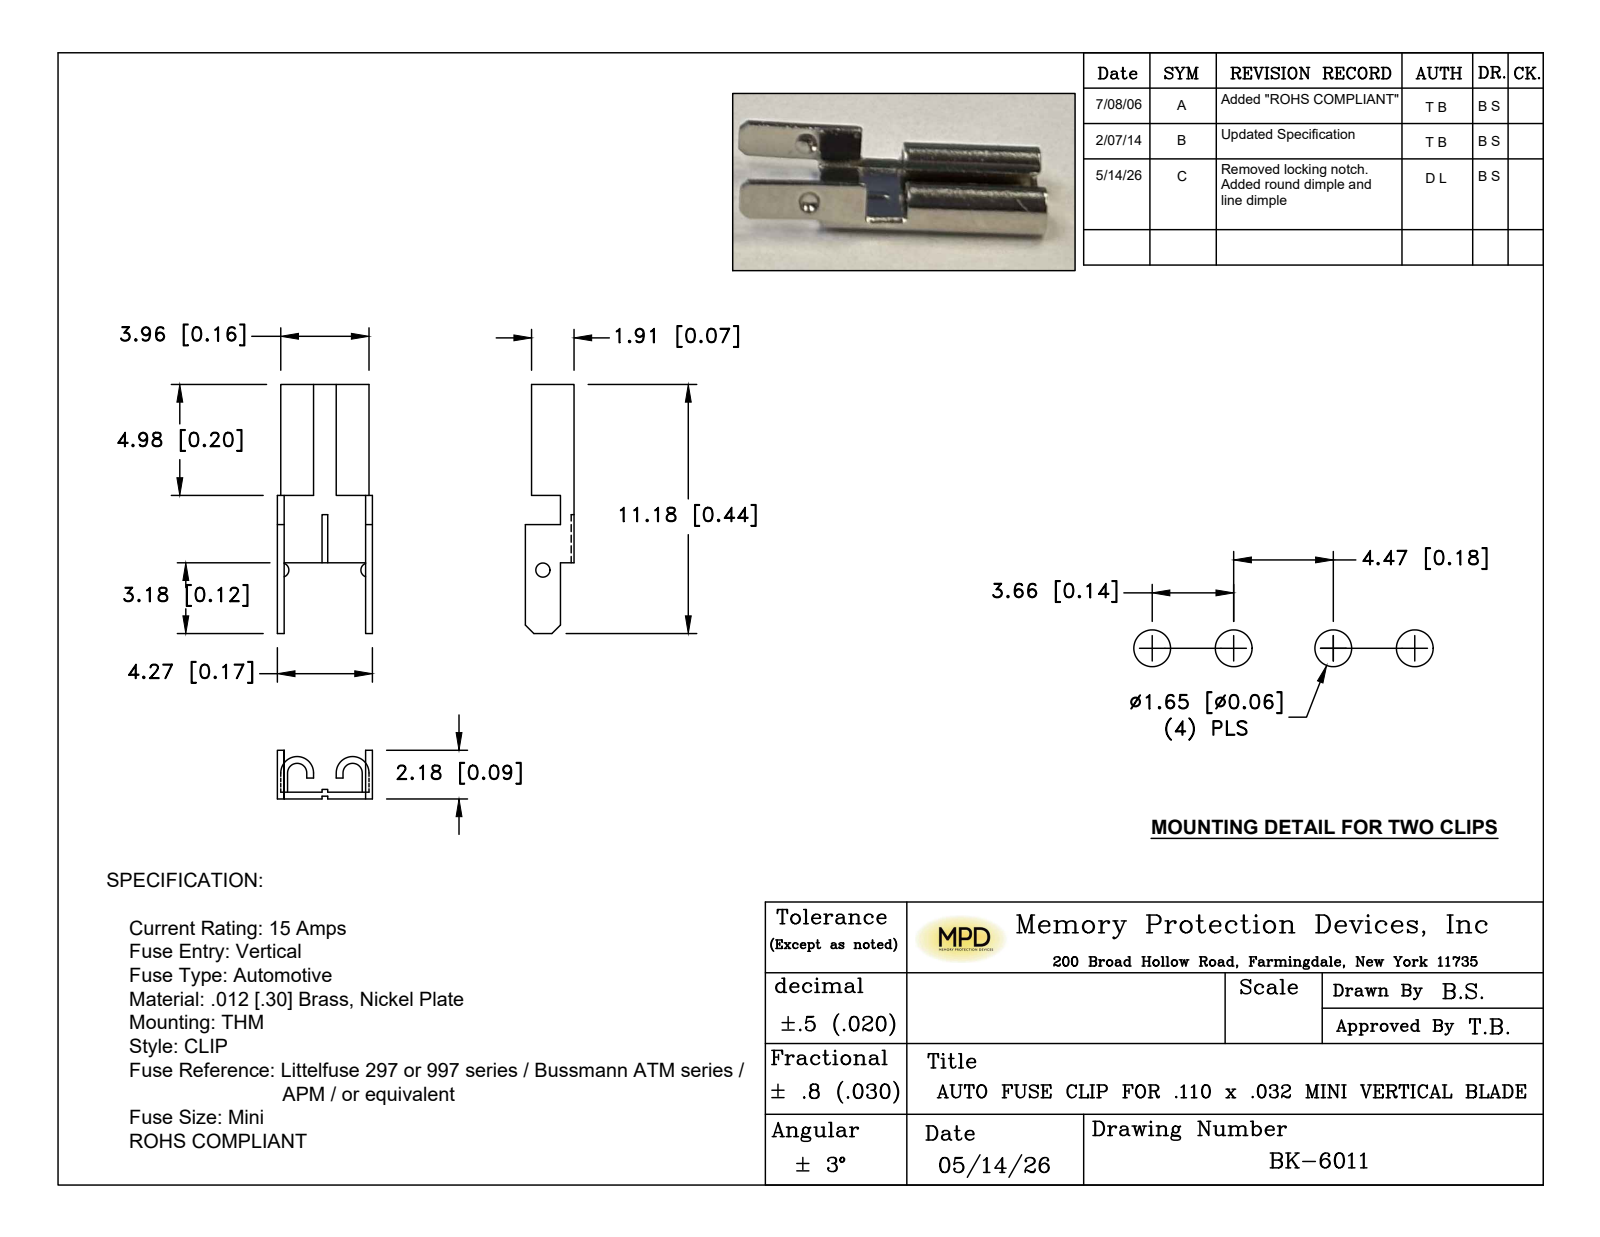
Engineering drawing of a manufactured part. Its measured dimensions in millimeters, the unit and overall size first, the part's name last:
Units: millimetres
Overall size (bounding box): 11.18 × 4.27 × 2.38
Partial cylindrical surfaces — rounded edges, fillets, slot ends (radius × count): R0.14 ×4, R0.45 ×4, R0.48 ×2, R0.79 ×2, R0.2 ×1, R0.51 ×1
Main face-to-face distances: 0.31, 3.97, 3.66, 4.28, 3.51, 0.46, 3.82, 4.12, 3.81, 1.28
Volume: 24 mm³ · Surface area: 175 mm²
Bodies: 1 solid, 84 faces (70 planar, 14 cylindrical, 0 other)
Part name (STEP PRODUCT): BK-6011
STEP written by: SolidWorks 2017 (AUTOMOTIVE_DESIGN)
